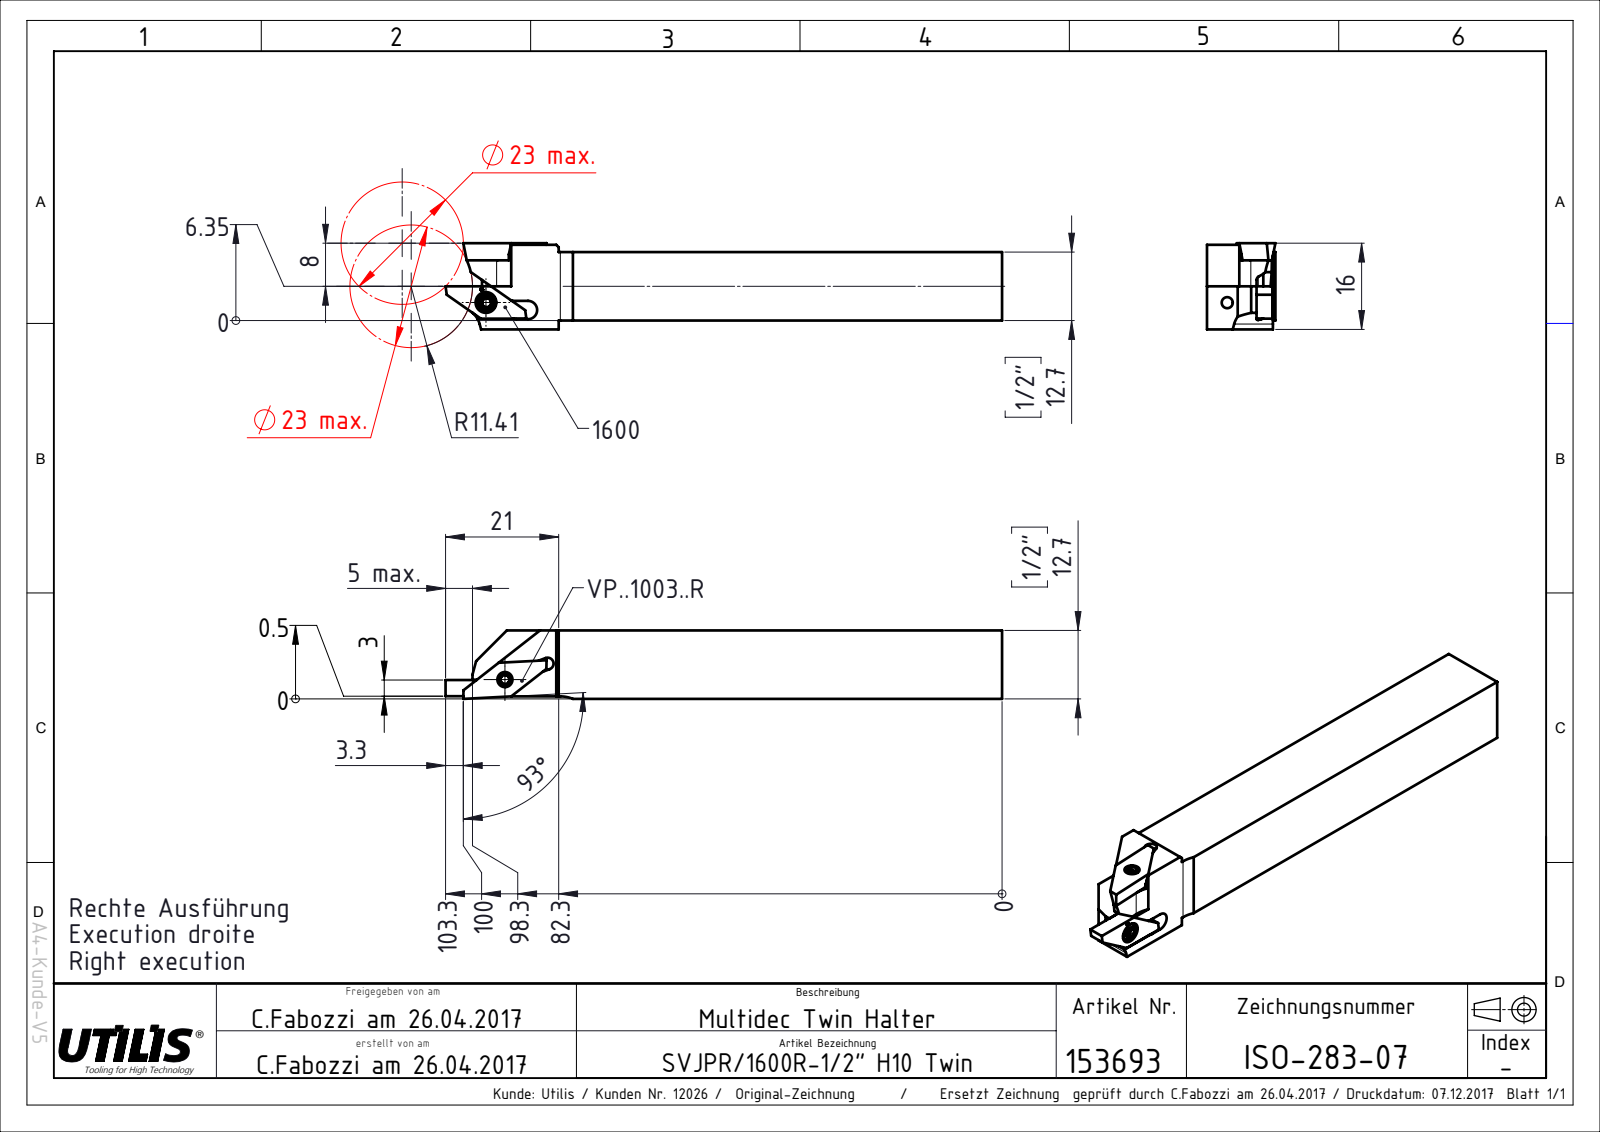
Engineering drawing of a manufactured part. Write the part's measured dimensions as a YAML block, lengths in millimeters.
part_name: "ISO-283-07"
step_written_by: "SolidWorks 2016 (AUTOMOTIVE_DESIGN)"
units: millimeters
bodies: {solids: 1, faces: 82, planar: 67, cylindrical: 13, other: 2}
overall_size: [103.3, 16, 12.7]
volume: 15660
surface_area: 5579
partial_cylinders:
  - {radius: 6.1, count: 3}
  - {radius: 0.25, count: 2}
  - {radius: 0.5, count: 1}
  - {radius: 1.1, count: 1}
  - {radius: 1.55, count: 1}
  - {radius: 1.7, count: 1}
  - {radius: 4.1, count: 1}
  - {radius: 11.41, count: 1}
face_to_face_distances: [12.7, 1.65, 14.35, 12.23, 0.47, 6.35, 8, 16, 15.7, 14.05]
